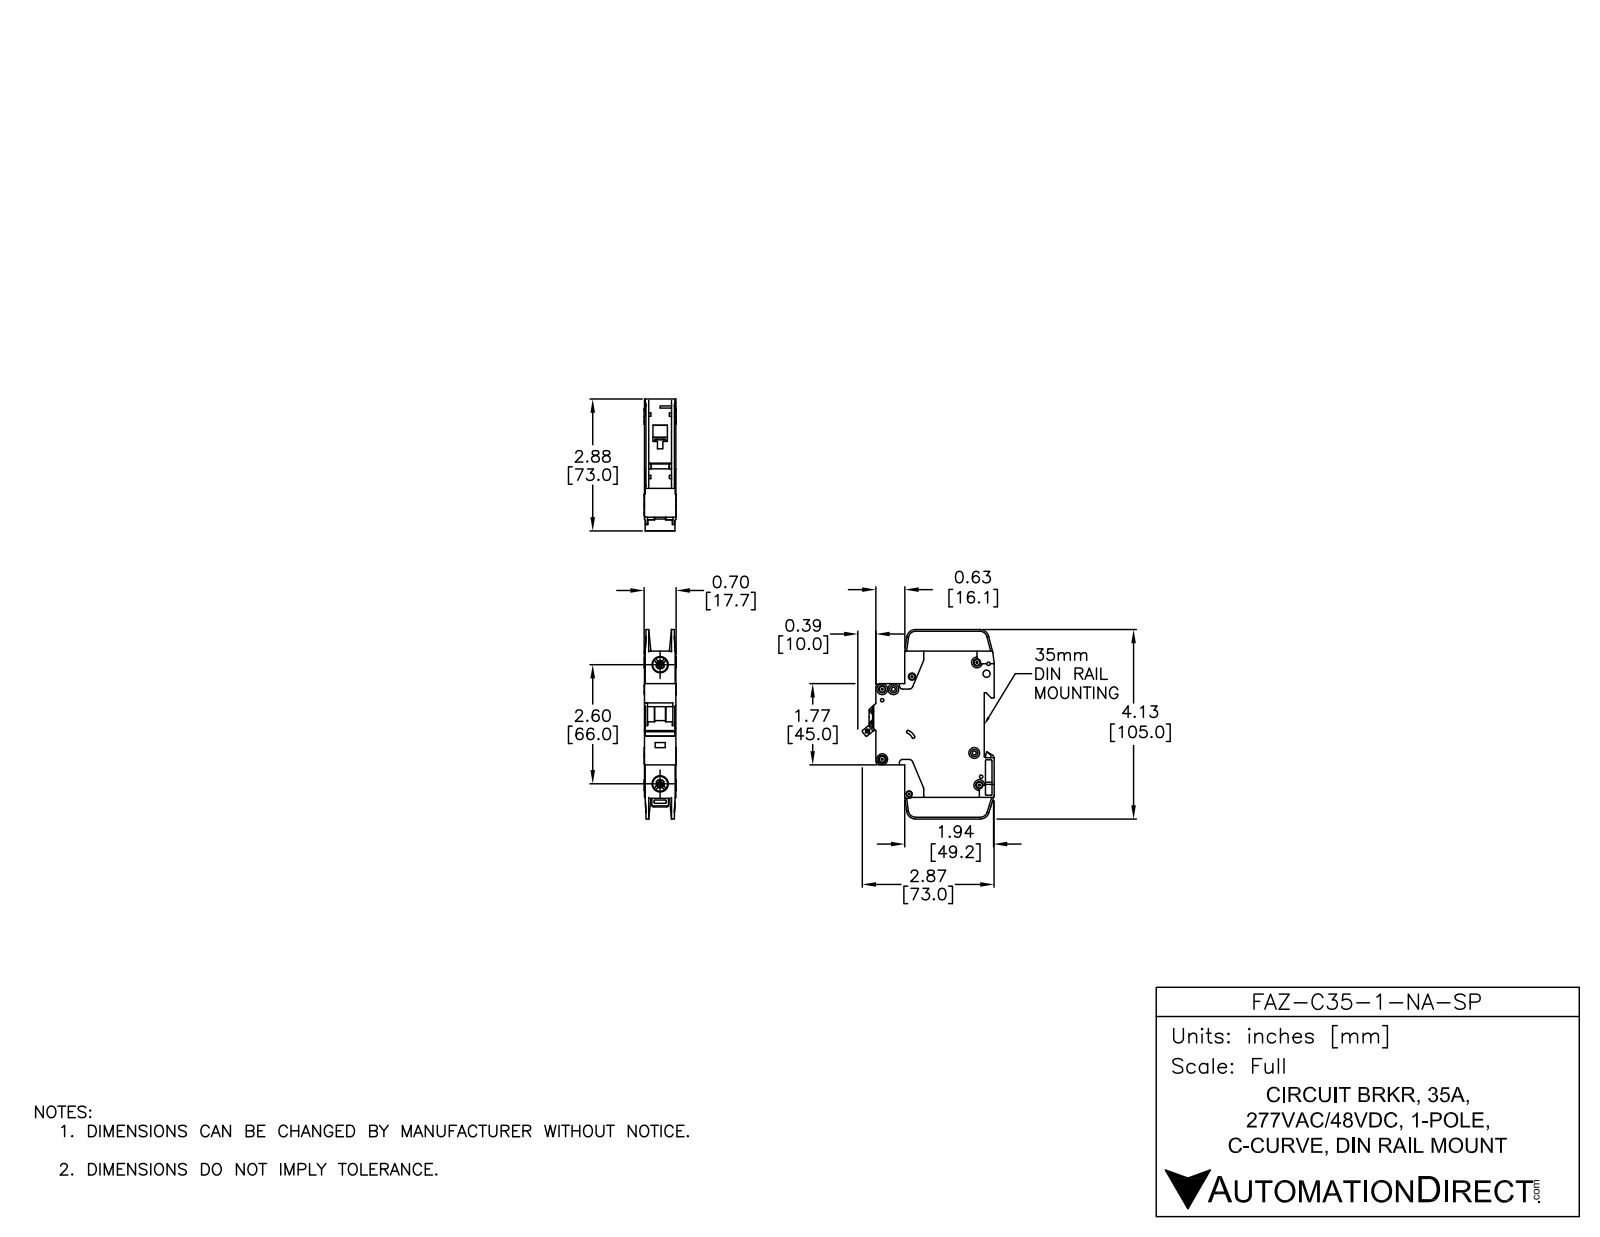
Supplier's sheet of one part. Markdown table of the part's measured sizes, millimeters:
| quantity | value |
| --- | --- |
| part name | FAZ-C35-1-NA-SP |
| STEP written by | SolidWorks 2014 (AUTOMOTIVE_DESIGN) |
| units | millimeters |
| bodies | 3 solids, 784 faces (409 planar, 263 cylindrical, 112 other) |
| overall size | 105 × 73.04 × 17.7 |
| volume | 77 695 mm³ |
| surface area | 24 740 mm² |
| round holes (diameter × count) | 3.6 × 7, 1.09 × 2, 1.5 × 2, 4 × 2, 7.15 × 2, 8.2 × 2, 1.9 × 1, 2.15 × 1, 2.2 × 1, 2.55 × 1, 3.3 × 1, 3.4 × 1 |
| round bosses / shafts (diameter × count) | 6 × 7, 2.5 × 1 |
| partial cylindrical surfaces (radius × count) | 0.25 × 29, 0.5 × 18, 1 × 10, 2 × 10, 5 × 5, 4 × 4, 1.8 × 3, 0.2 × 2 |
| main face-to-face distances | 17.5, 15.05, 0.7, 2.45, 1.75, 15.75, 13.3, 14, 12.6, 2 |
| hole center spacings | 6.2, 5.19, 6.1, 8.19, 8.56, 8.7, 11.11, 12.45 |
